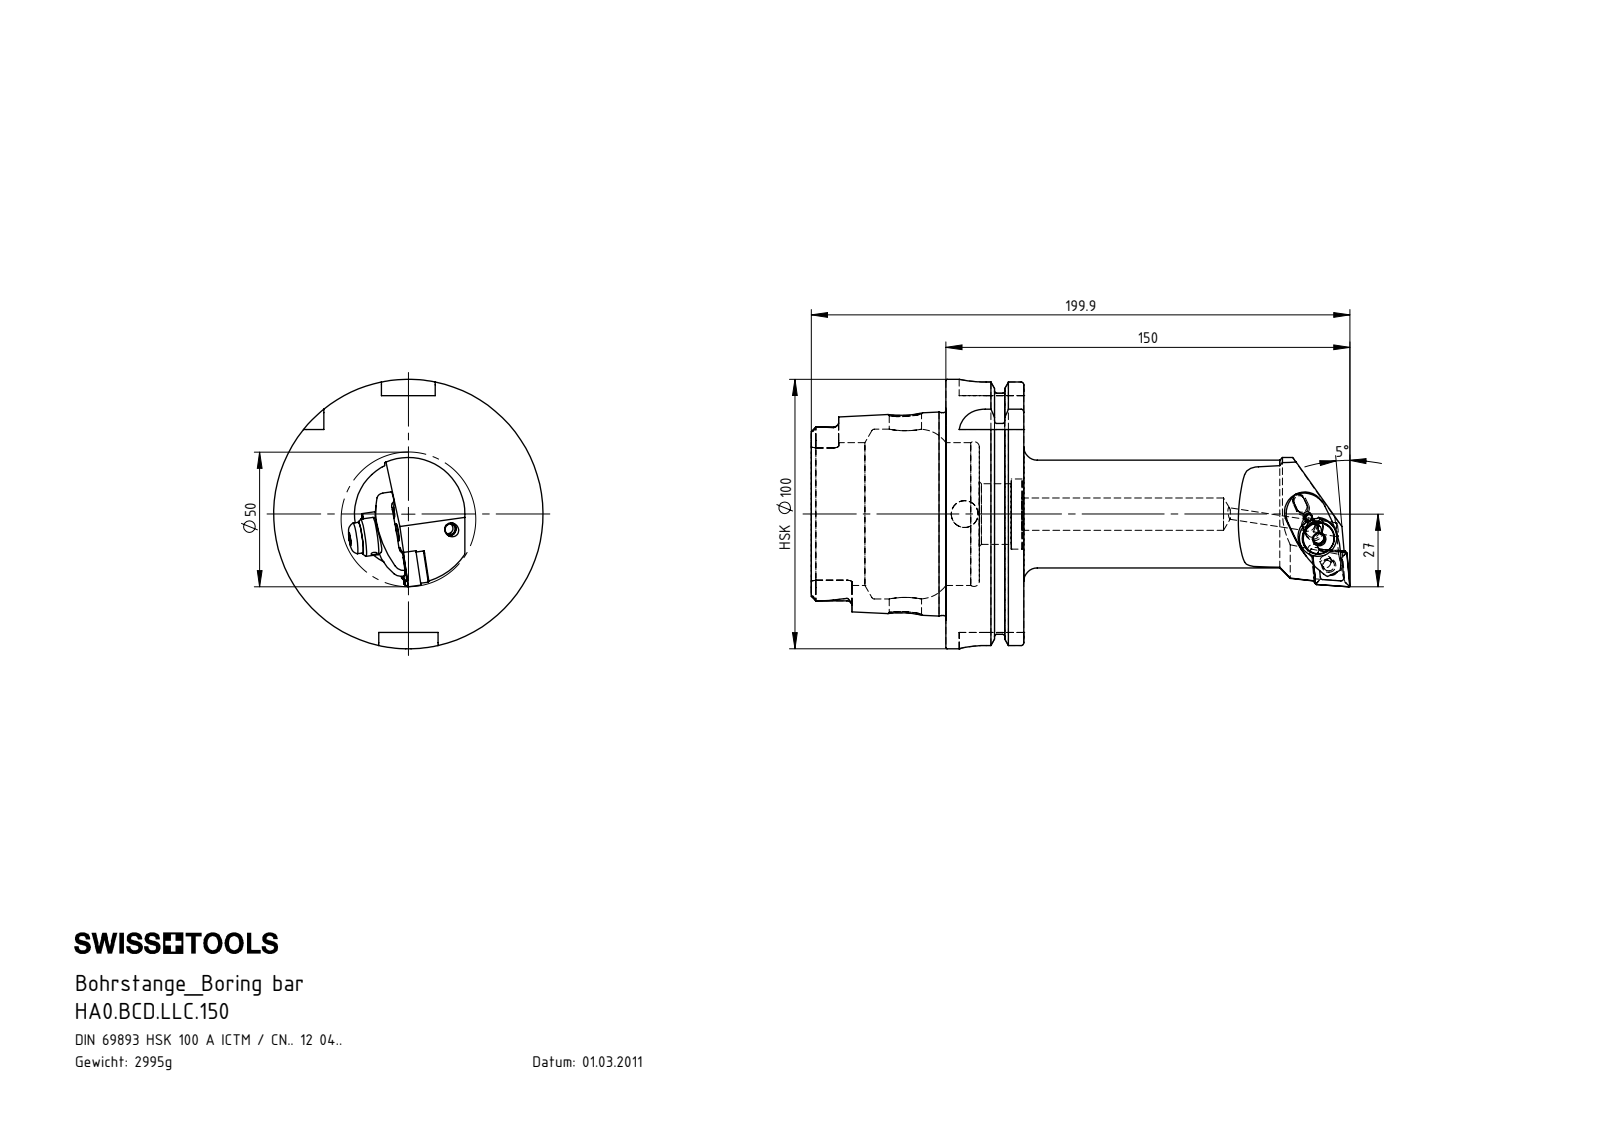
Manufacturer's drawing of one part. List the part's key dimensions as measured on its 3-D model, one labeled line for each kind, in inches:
Part name (STEP PRODUCT): WCD-ER2.101.003_A; ISO 13337 - 3 x 12_PreviewCfg; WCC-ER5.102.012_B; WCC-ER3.102.024_C (+6 more)
STEP written by: SolidWorks 2022 (AUTOMOTIVE_DESIGN)
Units: inches
Bodies: 10 solids, 458 faces (118 planar, 153 cylindrical, 187 other)
Overall size (bounding box): 7.87 × 3.937 × 3.937
Volume: 23.25 in³ · Surface area: 112.1 in²
Round holes (diameter × count): ⌀0.079 ×3, ⌀0.165 ×3, ⌀0.197 ×2, ⌀0.244 ×2, ⌀0.472 ×2, ⌀0.094 ×1, ⌀0.118 ×1, ⌀0.157 ×1, ⌀0.203 ×1, ⌀0.258 ×1, ⌀0.276 ×1, ⌀0.335 ×1
Round bosses / shafts (diameter × count): ⌀0.197 ×2, ⌀0.118 ×2, ⌀3.937 ×1, ⌀3.62 ×1, ⌀2.963 ×1, ⌀1.575 ×1, ⌀0.551 ×1, ⌀0.453 ×1
Partial cylindrical surfaces — rounded edges, fillets, slot ends (radius × count): R0.015 ×6, R0.027 ×6, R0.075 ×6, R0.016 ×4, R0.039 ×4, R0.394 ×4, R0.059 ×3, R0.079 ×2
Main face-to-face distances: 1.14, 0.49, 0.65, 1.965, 2.455, 3.104, 3.457, 3.079, 1.114, 0.624
Hole centre spacings: 0.903, 0.315, 0.323, 0.325, 0.58, 0.588, 0.588, 0.297
